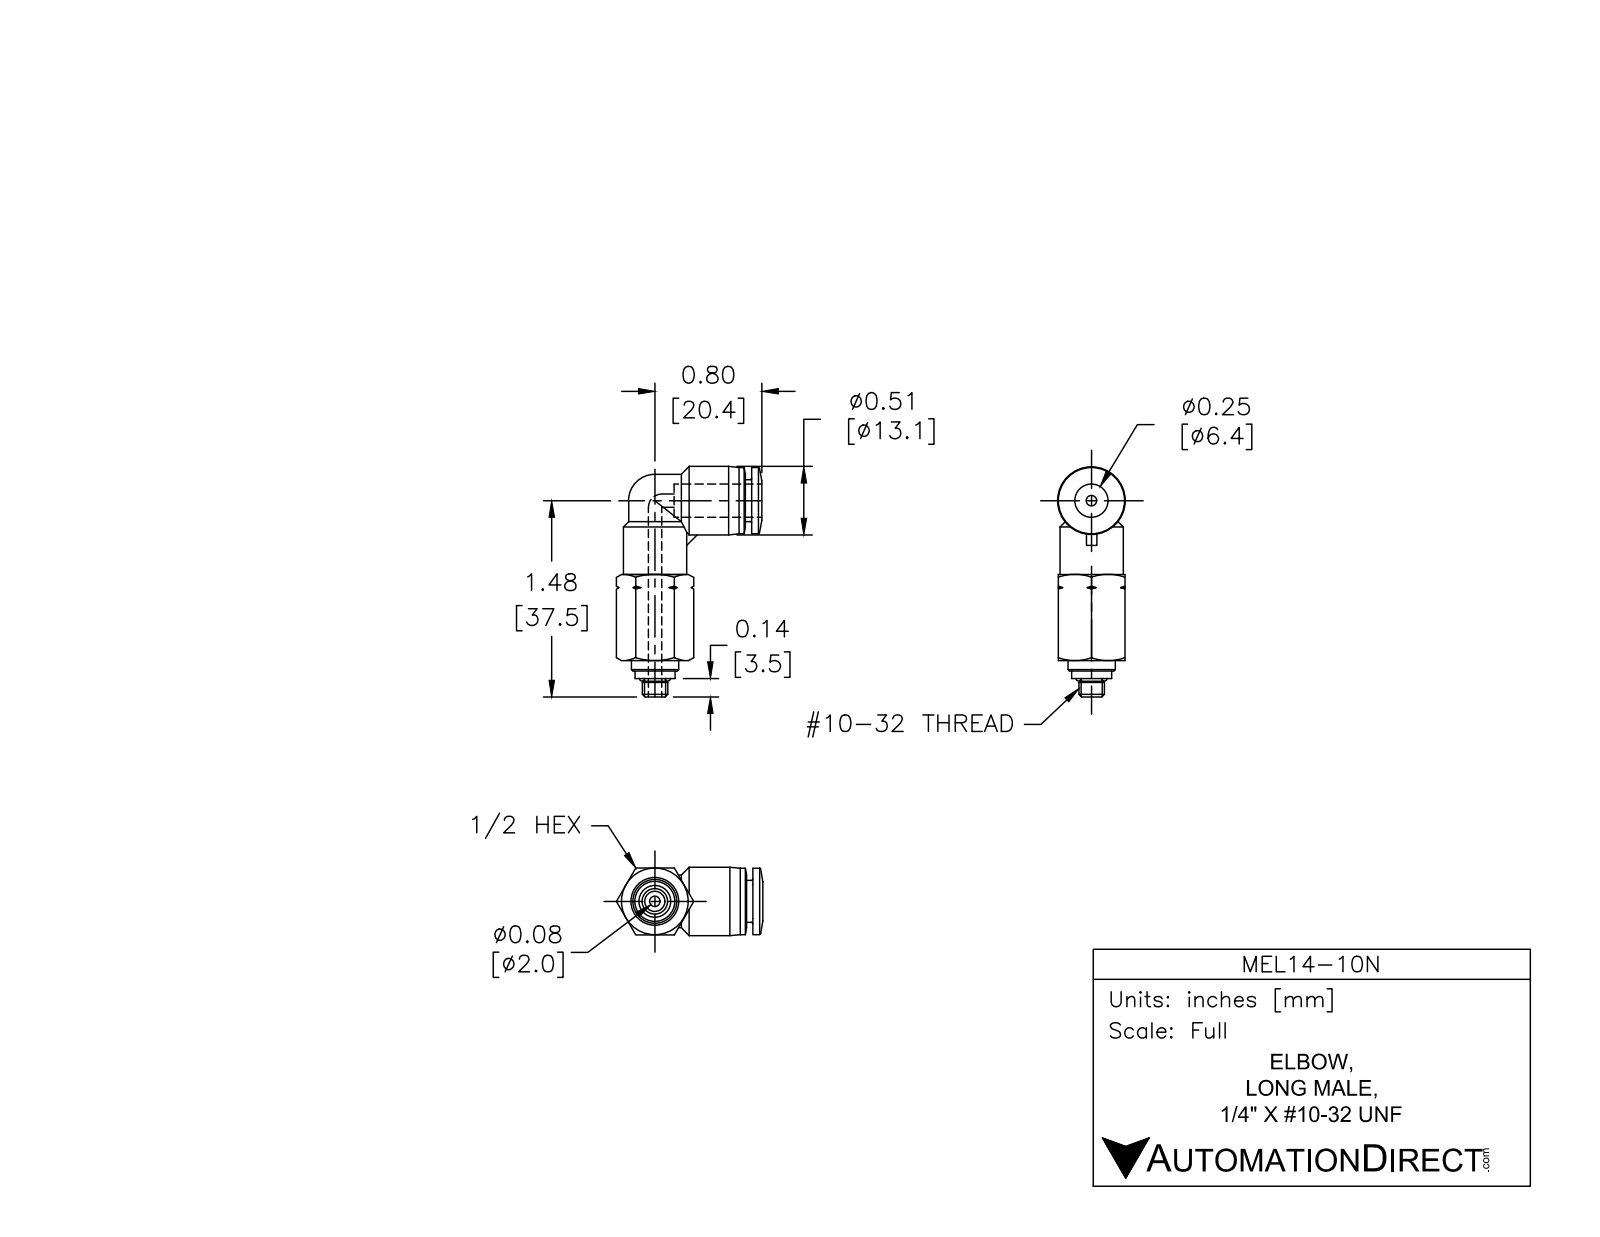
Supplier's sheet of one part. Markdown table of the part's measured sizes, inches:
| quantity | value |
| --- | --- |
| part name | MEL14-10N |
| STEP written by | SolidWorks 2015 (AUTOMOTIVE_DESIGN) |
| units | inches |
| bodies | 2 solids, 103 faces (18 planar, 28 cylindrical, 57 other) |
| overall size | 1.732 × 1.096 × 0.512 |
| volume | 0.345 in³ |
| surface area | 5.033 in² |
| round holes (diameter × count) | 0.079 × 2, 0.258 × 1 |
| round bosses / shafts (diameter × count) | 0.394 × 2, 0.512 × 1, 0.496 × 1, 0.472 × 1, 0.315 × 1, 0.313 × 1, 0.19 × 1, 0.156 × 1 |
| main face-to-face distances | 0.5, 0.587, 0.539, 0.047, 0.024, 0.752, 0.728, 0.031, 0.055, 0.783 |
